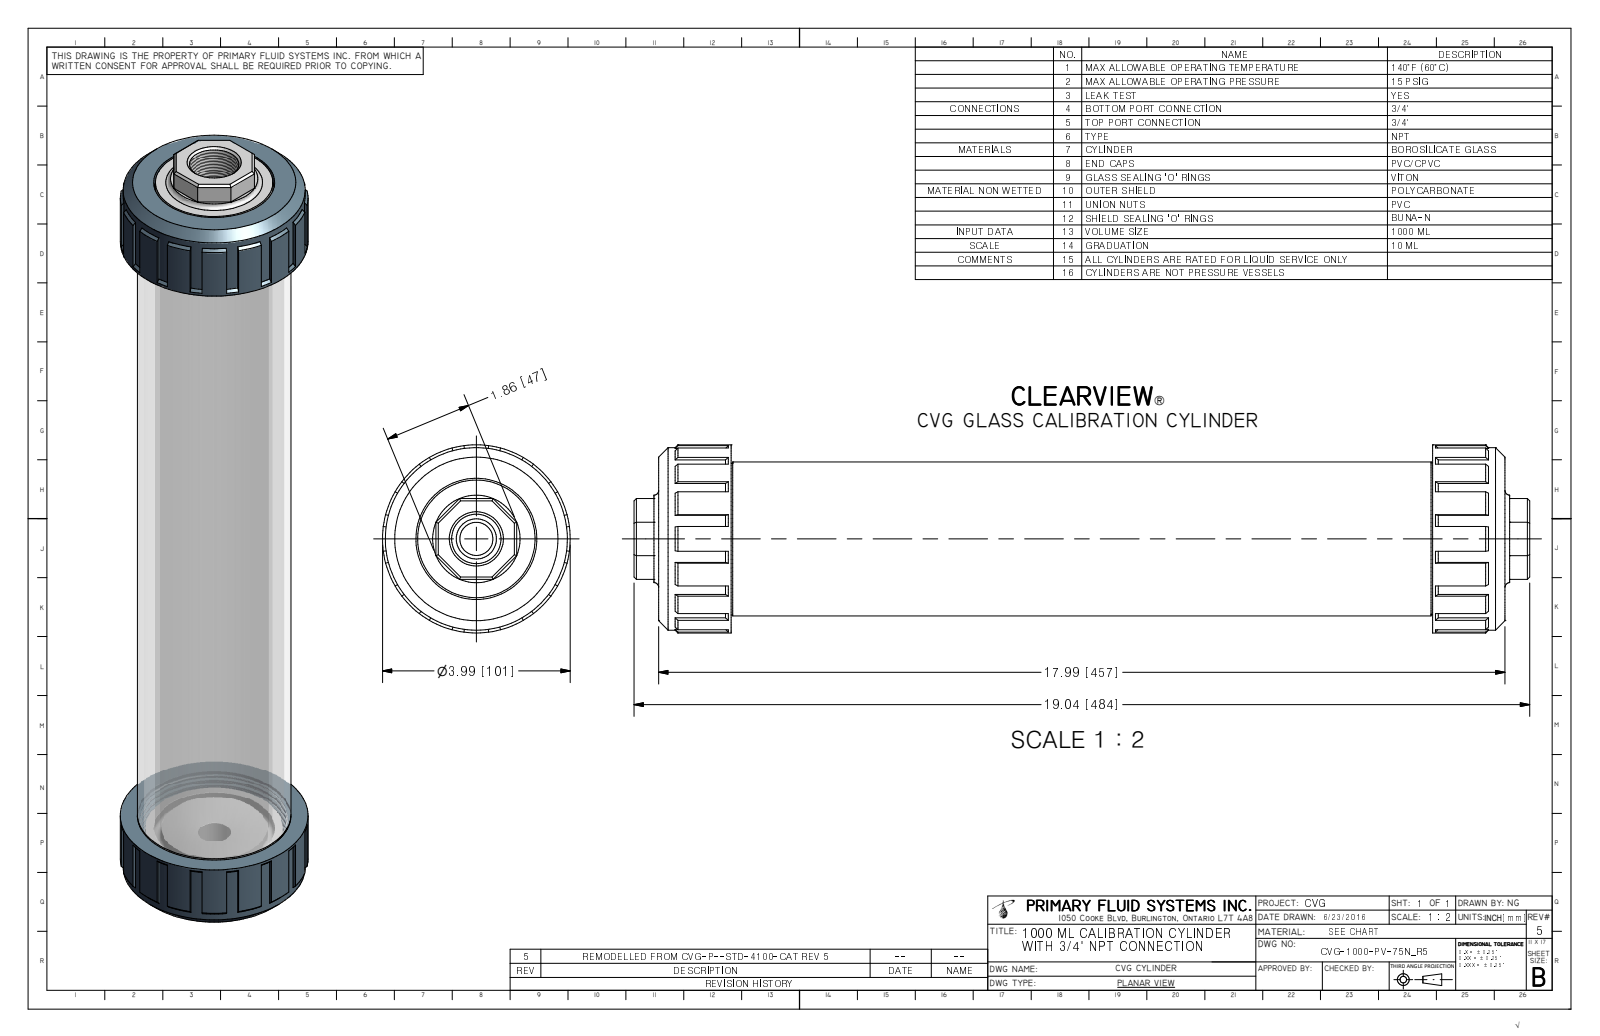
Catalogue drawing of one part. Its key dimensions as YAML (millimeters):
part_name: "CVG-1000-PVC-75N_R5; CVG-3-1000-POLY-NPT-75_R0; CVG-6-1000; CVG-1-1000-A_R0 (+1 more)"
step_written_by: "Autodesk Inventor 2009 (AUTOMOTIVE_DESIGN)"
units: millimeters
bodies: {solids: 6, faces: 356, planar: 162, cylindrical: 65, other: 129}
overall_size: [483.6, 101.3, 101.3]
volume: 1014000
surface_area: 489400
round_holes:
  - {diameter: 17.9, count: 1}
  - {diameter: 59.2, count: 1}
  - {diameter: 65.3, count: 1}
  - {diameter: 65.5, count: 1}
  - {diameter: 75.8, count: 1}
  - {diameter: 79.9, count: 1}
  - {diameter: 82.9, count: 1}
  - {diameter: 82.9, count: 1}
round_bosses_or_shafts:
  - {diameter: 101.3, count: 1}
  - {diameter: 98.3, count: 1}
  - {diameter: 81.9, count: 1}
  - {diameter: 78.9, count: 1}
  - {diameter: 78.3, count: 1}
  - {diameter: 74.4, count: 1}
  - {diameter: 71.7, count: 1}
  - {diameter: 64, count: 1}
face_to_face_distances: [39.1, 417.9, 410.3, 7.6, 449.4, 31.5, 457, 378.8, 441.8, 31.1]
